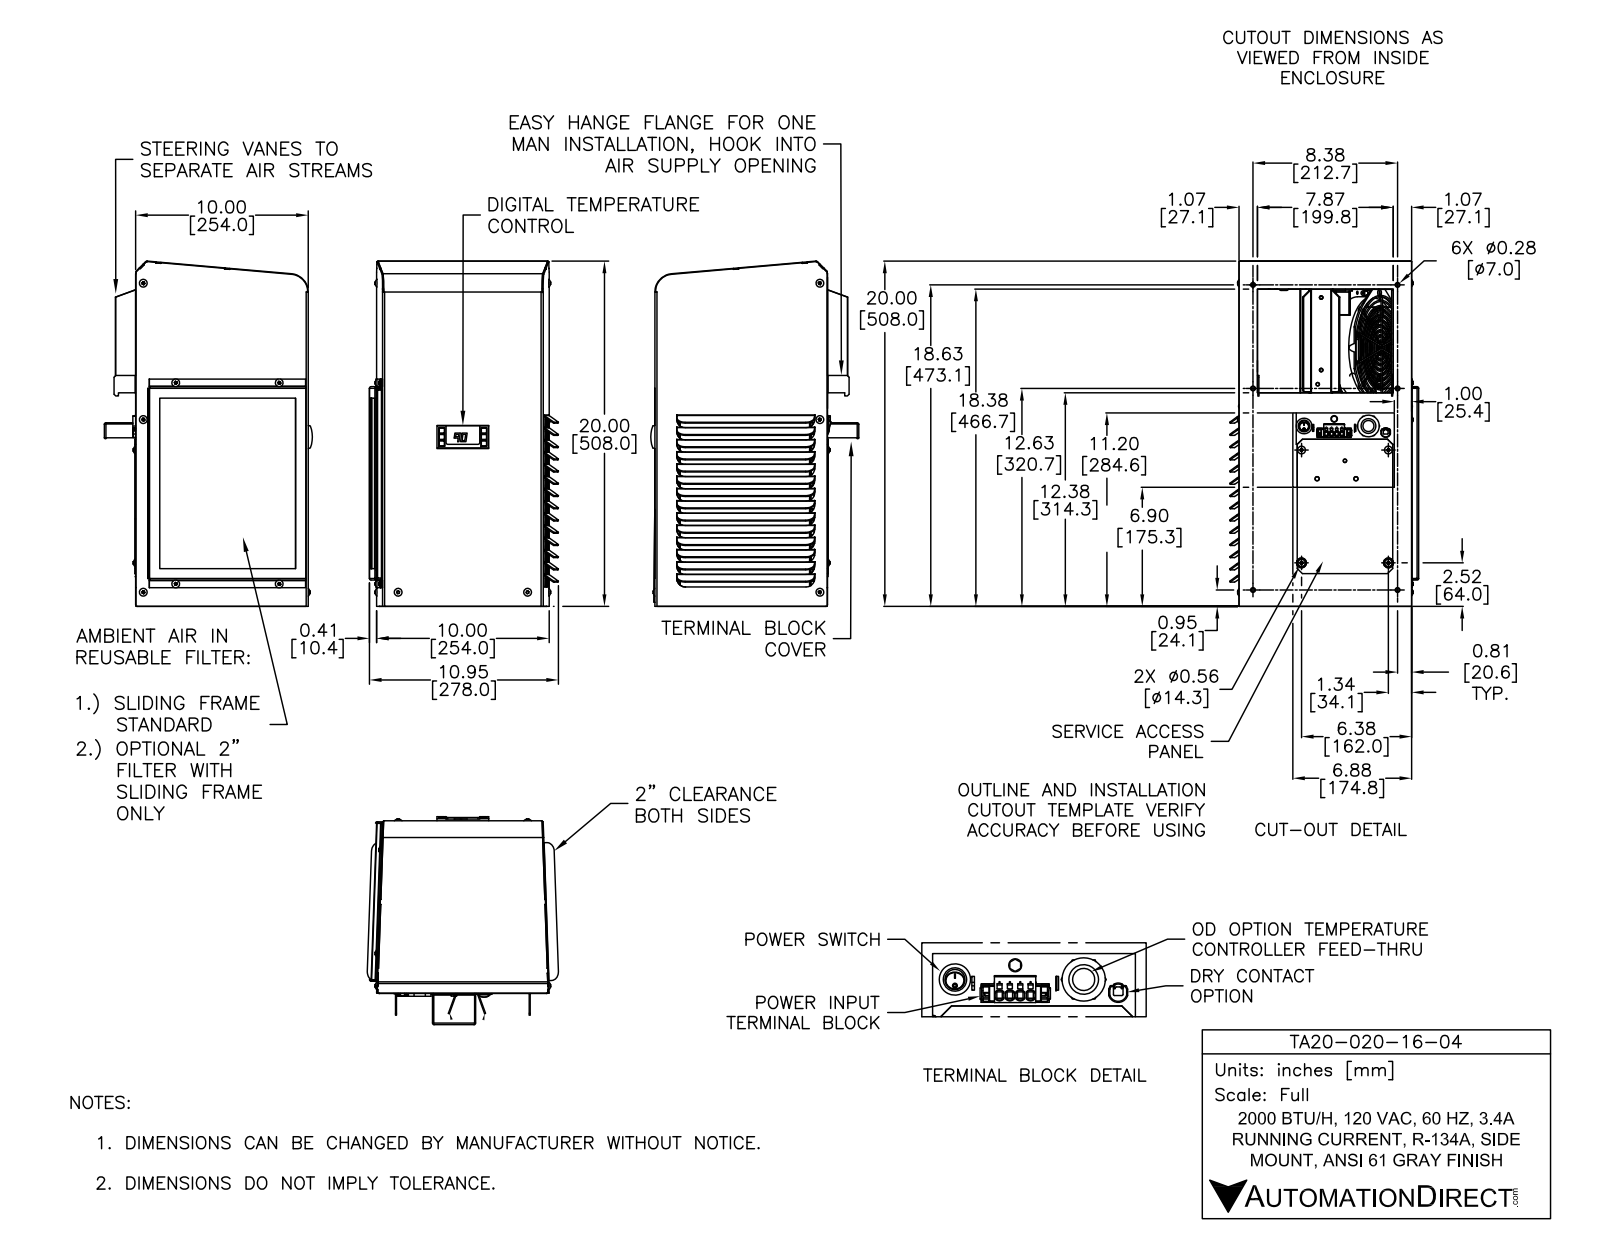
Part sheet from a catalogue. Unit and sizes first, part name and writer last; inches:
Units: inches
Overall size (bounding box): 20 × 11.344 × 11.002
Round holes (diameter × count): ⌀0.204 ×17, ⌀0.2 ×6, ⌀0.344 ×6, ⌀0.045 ×4, ⌀0.12 ×4, ⌀0.14 ×4, ⌀0.166 ×4, ⌀0.219 ×4, ⌀0.091 ×2, ⌀0.126 ×2, ⌀0.166 ×2, ⌀0.25 ×2
Round bosses / shafts (diameter × count): ⌀0.19 ×16, ⌀0.44 ×6, ⌀0.36 ×2, ⌀0.106 ×2, ⌀1 ×1, ⌀0.906 ×1, ⌀0.865 ×1, ⌀0.832 ×1
Partial cylindrical surfaces — rounded edges, fillets, slot ends (radius × count): R0.015 ×100, R0.01 ×96, R0.031 ×44, R0.03 ×33, R0.1 ×22, R0.011 ×16, R0.091 ×14, R0.089 ×13
Main face-to-face distances: 0.06, 0.058, 10, 9.94, 9.942, 9.882, 0.185, 0.244, 2.624, 2.809
Hole centre spacings: 0.2, 0.4, 6, 6, 11.65, 13.104, 8.251, 8.375
Volume: 401.3 in³ · Surface area: 2 755 in²
Bodies: 52 solids, 2157 faces (1121 planar, 737 cylindrical, 299 other)
Part name (STEP PRODUCT): TA20-020-16-04
STEP written by: SolidWorks 2019 (AUTOMOTIVE_DESIGN)
